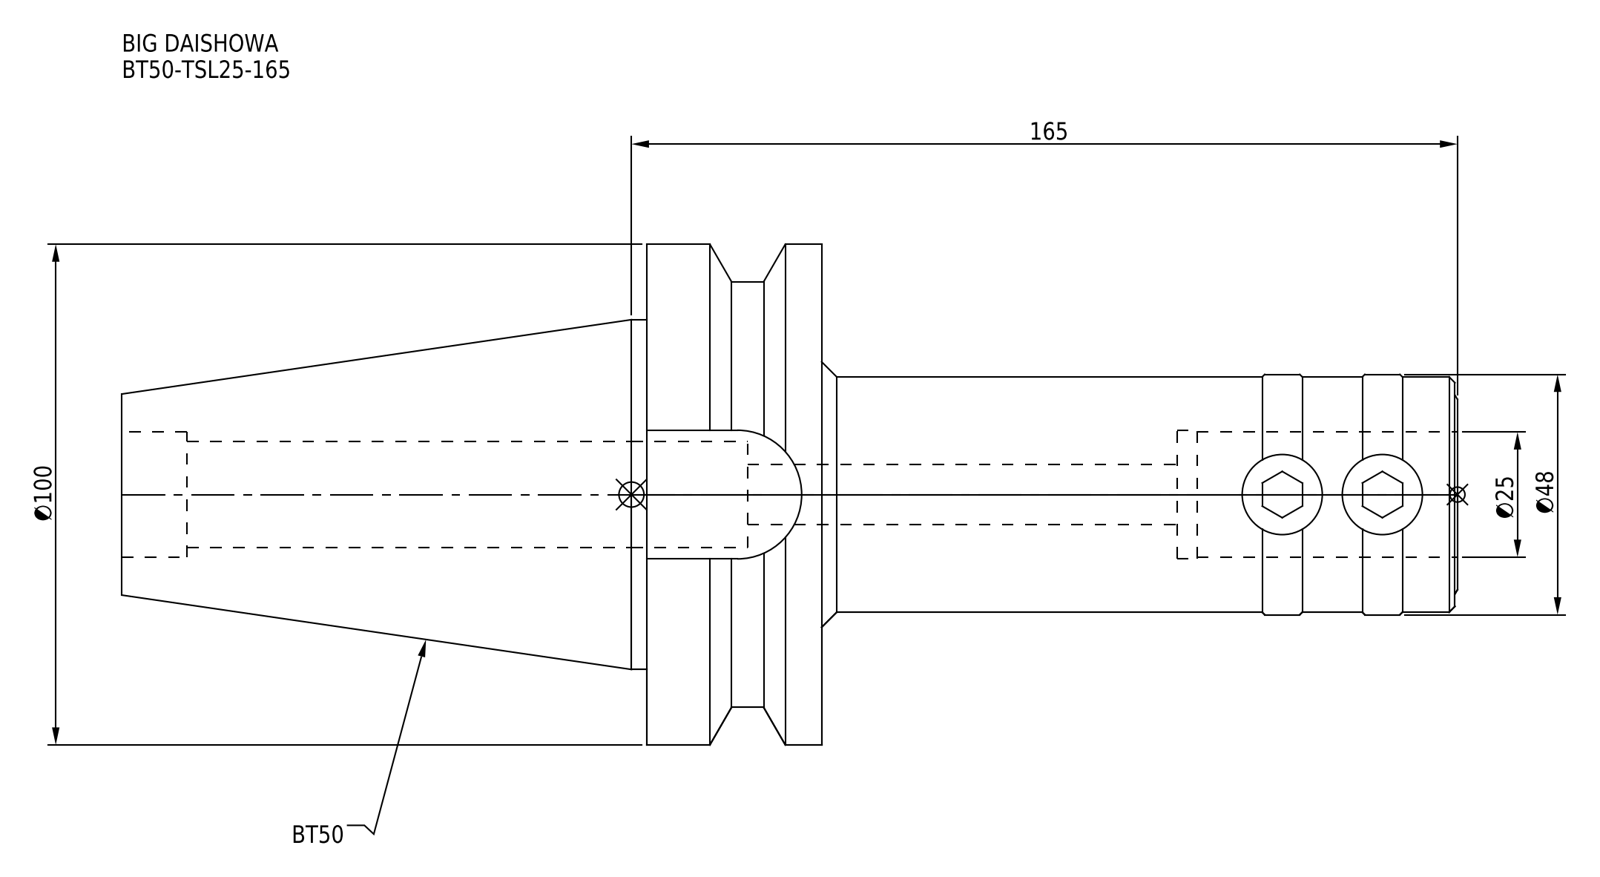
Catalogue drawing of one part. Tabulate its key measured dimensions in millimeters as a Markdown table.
| quantity | value |
| --- | --- |
| part name | BT50-TSL25-165 |
| STEP written by | CREO PARAMETRIC BY PTC INC, 2016380 (AUTOMOTIVE_DESIGN) |
| units | millimeters |
| bodies | 1 solid, 67 faces (15 planar, 32 cylindrical, 20 other) |
| overall size | 266.8 × 100 × 100 |
| volume | 632 602 mm³ |
| surface area | 79 593 mm² |
| round holes (diameter × count) | 12 × 1, 21.2 × 1, 25 × 1, 25.6 × 1 |
| round bosses / shafts (diameter × count) | 100 × 1, 85 × 1, 69.85 × 1, 48 × 1, 47 × 1 |
| partial cylindrical surfaces (radius × count) | 12.85 × 1 |
| main face-to-face distances | 35, 139.8, 104.8, 70.8, 127, 162, 266.8, 25.7, 56, 71 |
